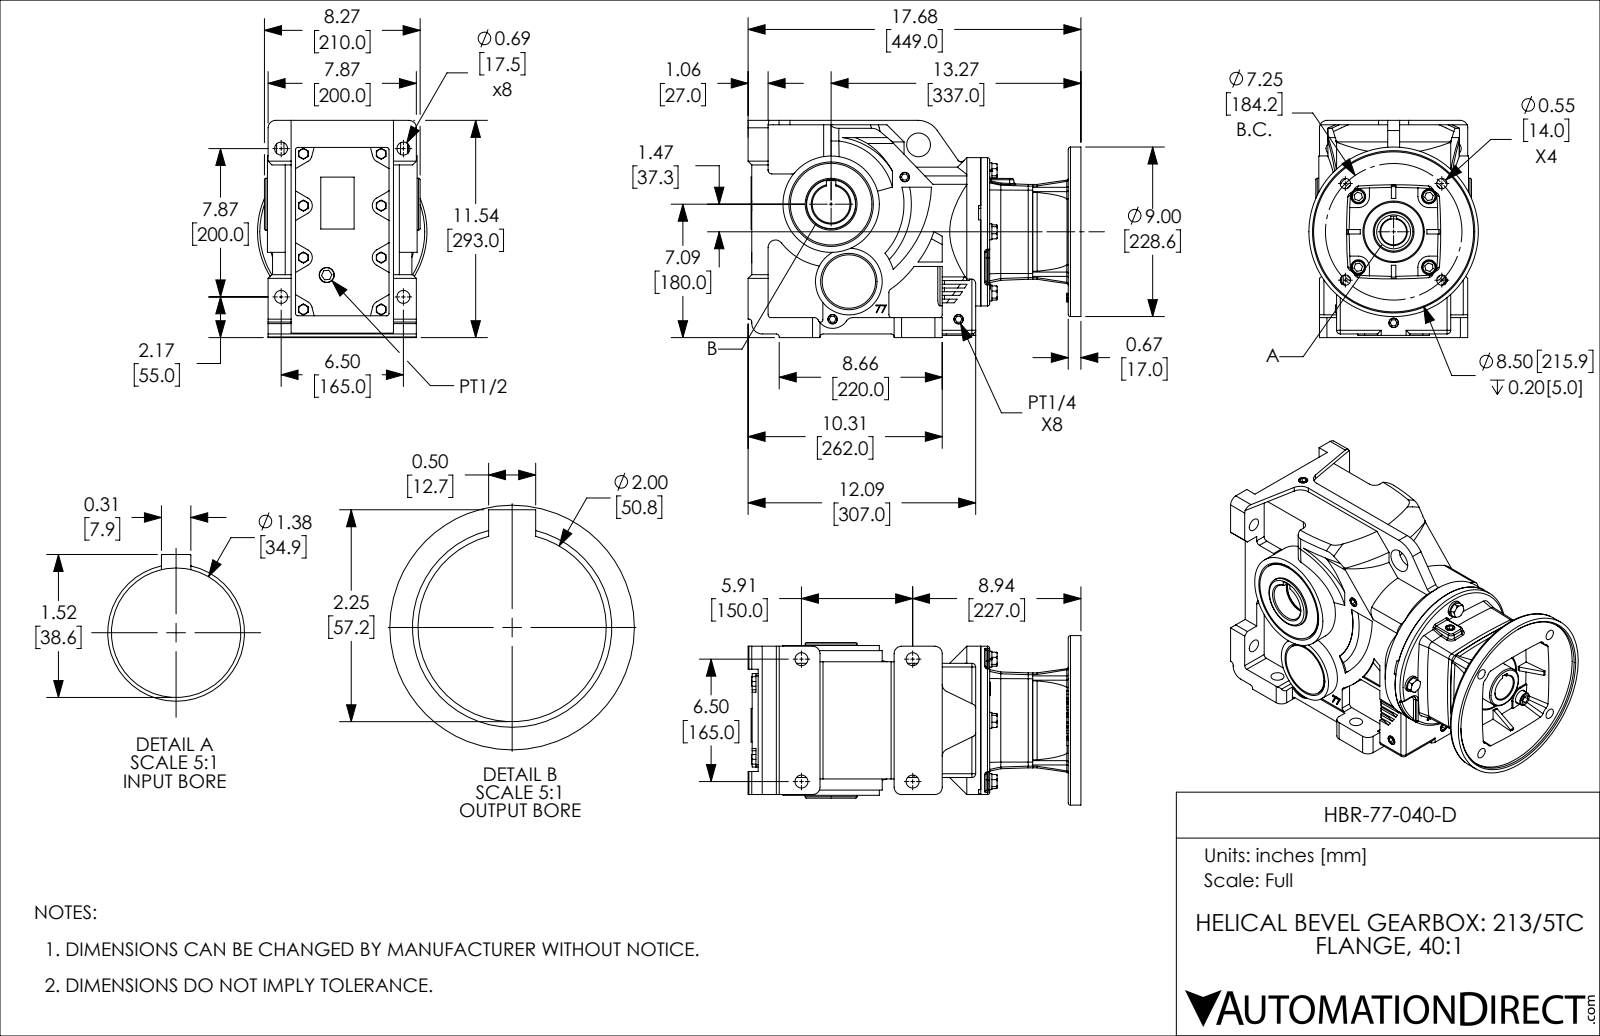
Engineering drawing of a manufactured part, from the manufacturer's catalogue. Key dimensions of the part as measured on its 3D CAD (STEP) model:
Part name (STEP PRODUCT): HBR-77-040-D
STEP written by: SolidWorks 2018 (AUTOMOTIVE_DESIGN)
Units: inches
Bodies: 43 solids, 1785 faces (759 planar, 598 cylindrical, 428 other)
Overall size (bounding box): 17.677 × 11.535 × 9
Volume: 374.3 in³ · Surface area: 1 991 in²
Round holes (diameter × count): ⌀0.268 ×8, ⌀0.354 ×8, ⌀0.689 ×8, ⌀0.335 ×4, ⌀0.402 ×4, ⌀0.433 ×4, ⌀0.472 ×4, ⌀0.48 ×4, ⌀0.512 ×4, ⌀0.551 ×4, ⌀0.787 ×4, ⌀0.438 ×3
Round bosses / shafts (diameter × count): ⌀0.315 ×8, ⌀0.846 ×4, ⌀0.709 ×4, ⌀0.394 ×4, ⌀5.118 ×2, ⌀0.827 ×2, ⌀9 ×1, ⌀7.874 ×1
Partial cylindrical surfaces — rounded edges, fillets, slot ends (radius × count): R0.394 ×37, R0.079 ×16, R0.591 ×15, R0.472 ×14, R0.197 ×12, R0.315 ×12, R0.118 ×9, R0.236 ×9
Main face-to-face distances: 0.236, 0.472, 0.315, 4.961, 0.787, 0.276, 5.748, 5.276, 0.512, 0.551
Hole centre spacings: 2.325, 5.461, 2.653, 2.756, 4.495, 4.968, 6.352, 6.496
